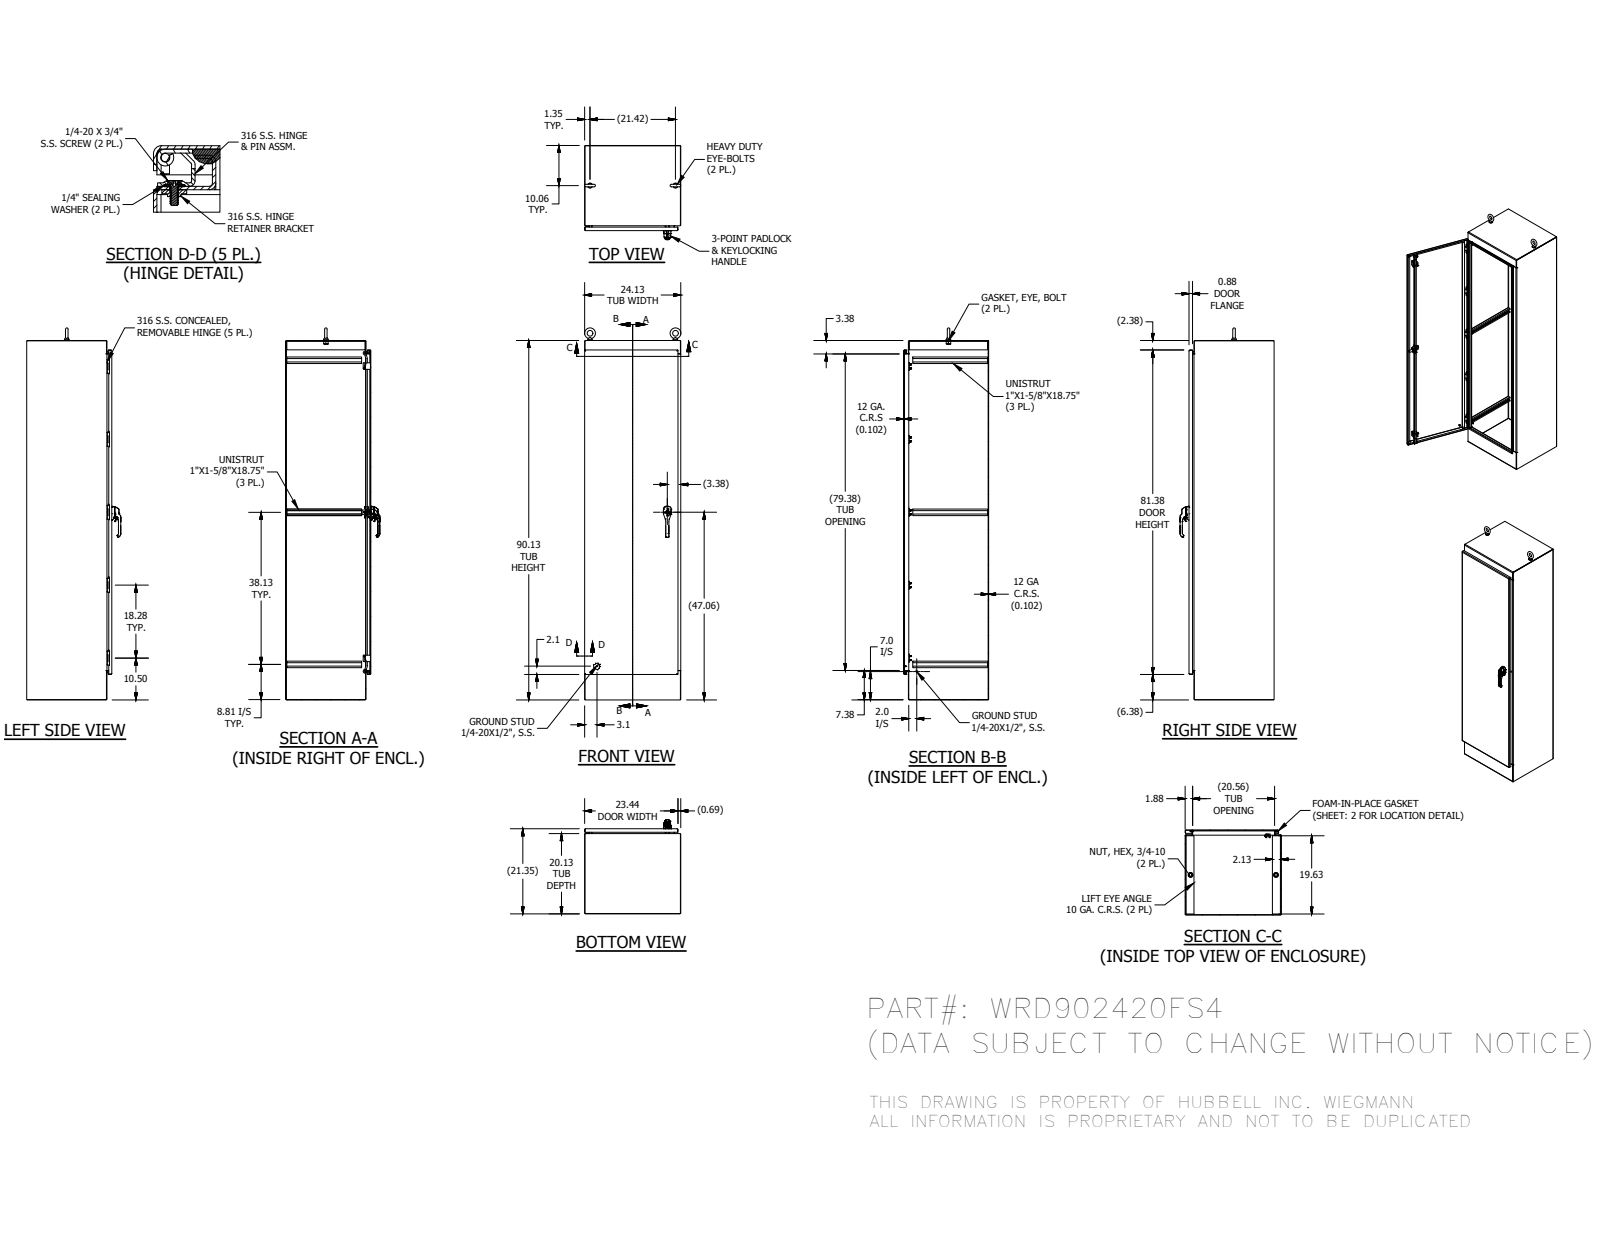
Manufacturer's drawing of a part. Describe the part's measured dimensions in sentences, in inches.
The part is named "WRD902420FS4BLR; WRD2420FS4TOP; WRD2420FS4BTM; WRD9024FS4DR (+8 more)". Its 3-D file was written by "Autodesk Inventor 2016 (AUTOMOTIVE_DESIGN)". It is 94 solids with 3853 faces: 1592 planar, 1281 cylindrical and 980 other. Overall it measures 93.248 by 24.127 by 23.616 inches. Its volume is 1 136 cubic inches and its surface area 21 680 square inches. Round holes: 10 of diameter 0.23, 10 of diameter 0.281, 10 of diameter 0.65, 8 of diameter 0.276, 4 of diameter 0.2, 3 of diameter 0.213, 3 of diameter 0.236, 3 of diameter 0.28, 2 of diameter 0.241, 2 of diameter 0.25, 2 of diameter 0.252, 2 of diameter 0.4. Round bosses or shafts: 18 of diameter 0.25, 10 of diameter 0.625, 10 of diameter 0.404, 10 of diameter 0.182, 2 of diameter 1.25, 2 of diameter 1.12, 2 of diameter 1, 2 of diameter 0.75. Partial cylindrical surfaces (rounded edges, fillets, slot ends): 165 of radius 0.02, 84 of radius 0.012, 33 of radius 0.063, 26 of radius 0.01, 22 of radius 0.125, 19 of radius 0.019, 15 of radius 0.079, 14 of radius 0.05. The main face-to-face distances are 0.102, 21.245, 24.023, 21.143, 23.921, 21.347, 24.125, 90.023, 20.023, 1.222. The hole center spacings are 1, 0.492, 18.281, 18.281, 36.563, 54.844, 0.256, 0.886.
